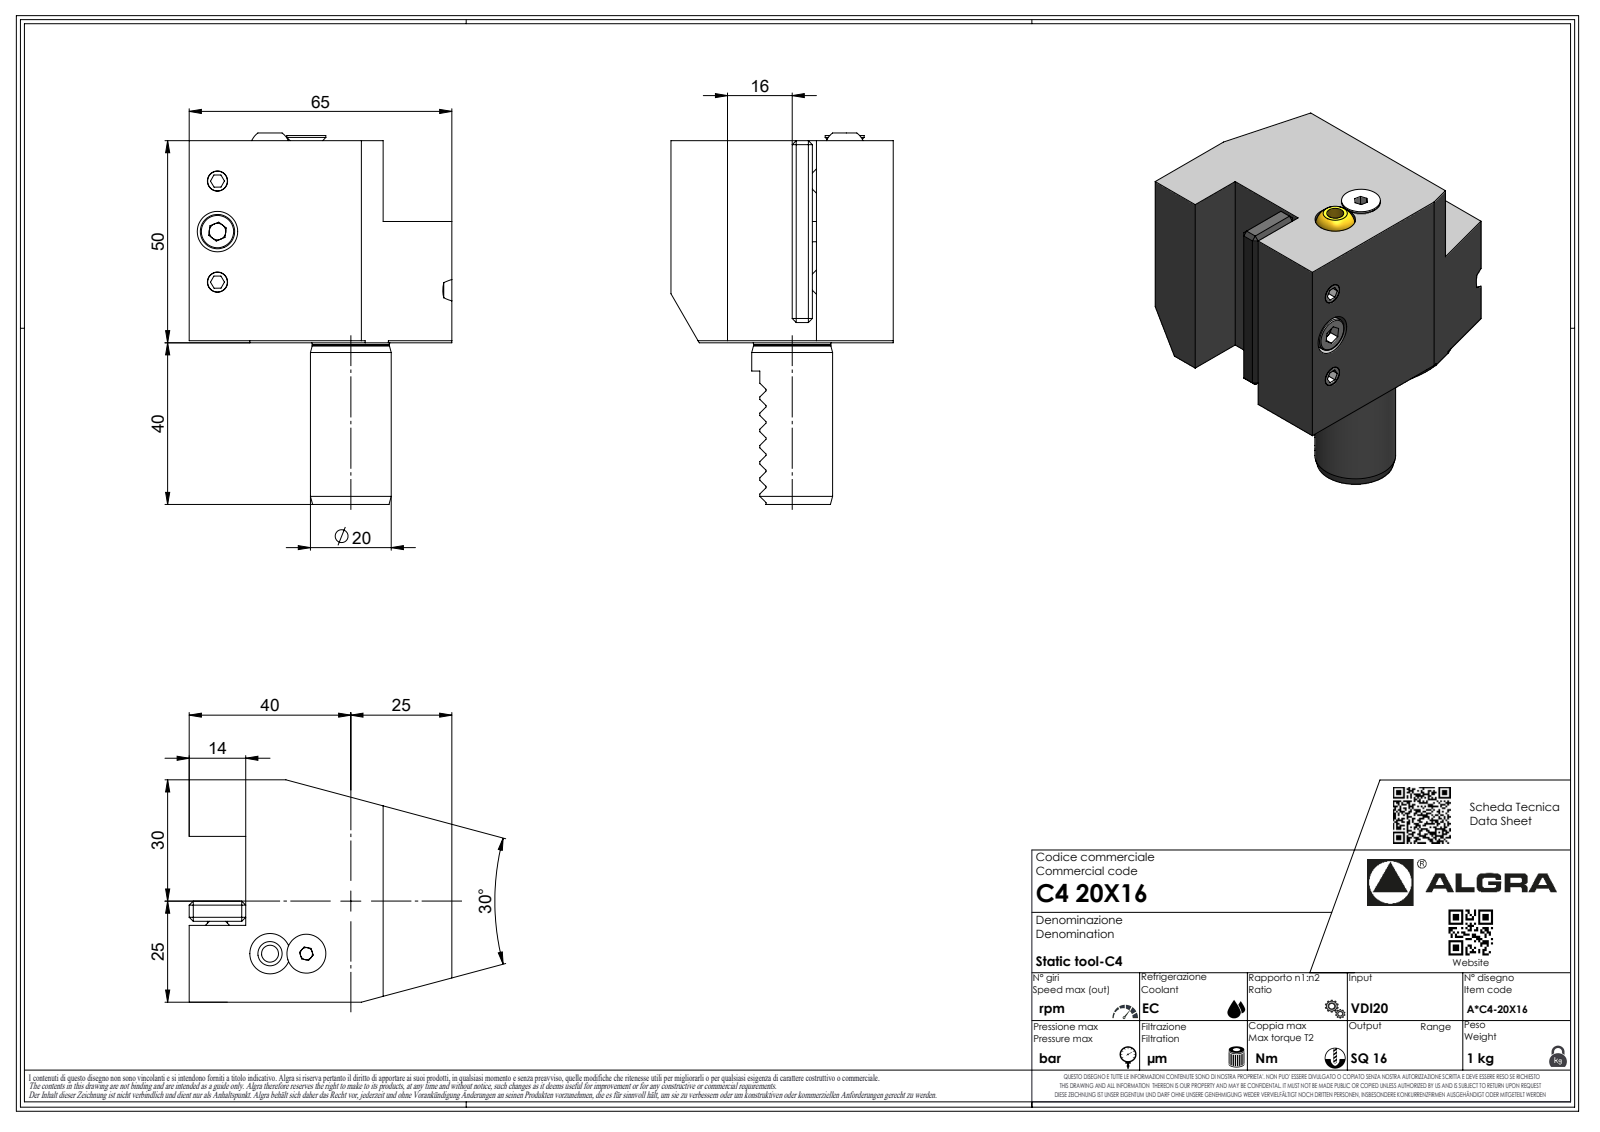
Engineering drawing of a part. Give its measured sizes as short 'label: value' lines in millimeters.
name: C420X16
written by: SolidWorks 2023 (AUTOMOTIVE_DESIGN)
unit: mm
bodies: 1 solid, 296 faces (213 planar, 39 cylindrical, 44 other)
size: 91.89 × 65 × 55
volume: 147 198 mm³; area: 21 944 mm²
holes: 1× ⌀2.1
bosses: 1× ⌀50, 1× ⌀20, 1× ⌀19.1, 1× ⌀6.37, 1× ⌀5, 1× ⌀1.7
rounds: 8× R0.3, 7× R0.33, 7× R0.52, 7× R3.7, 1× R0.21
face distances: 14, 50, 30, 20, 65, 51, 17, 34, 48, 55
